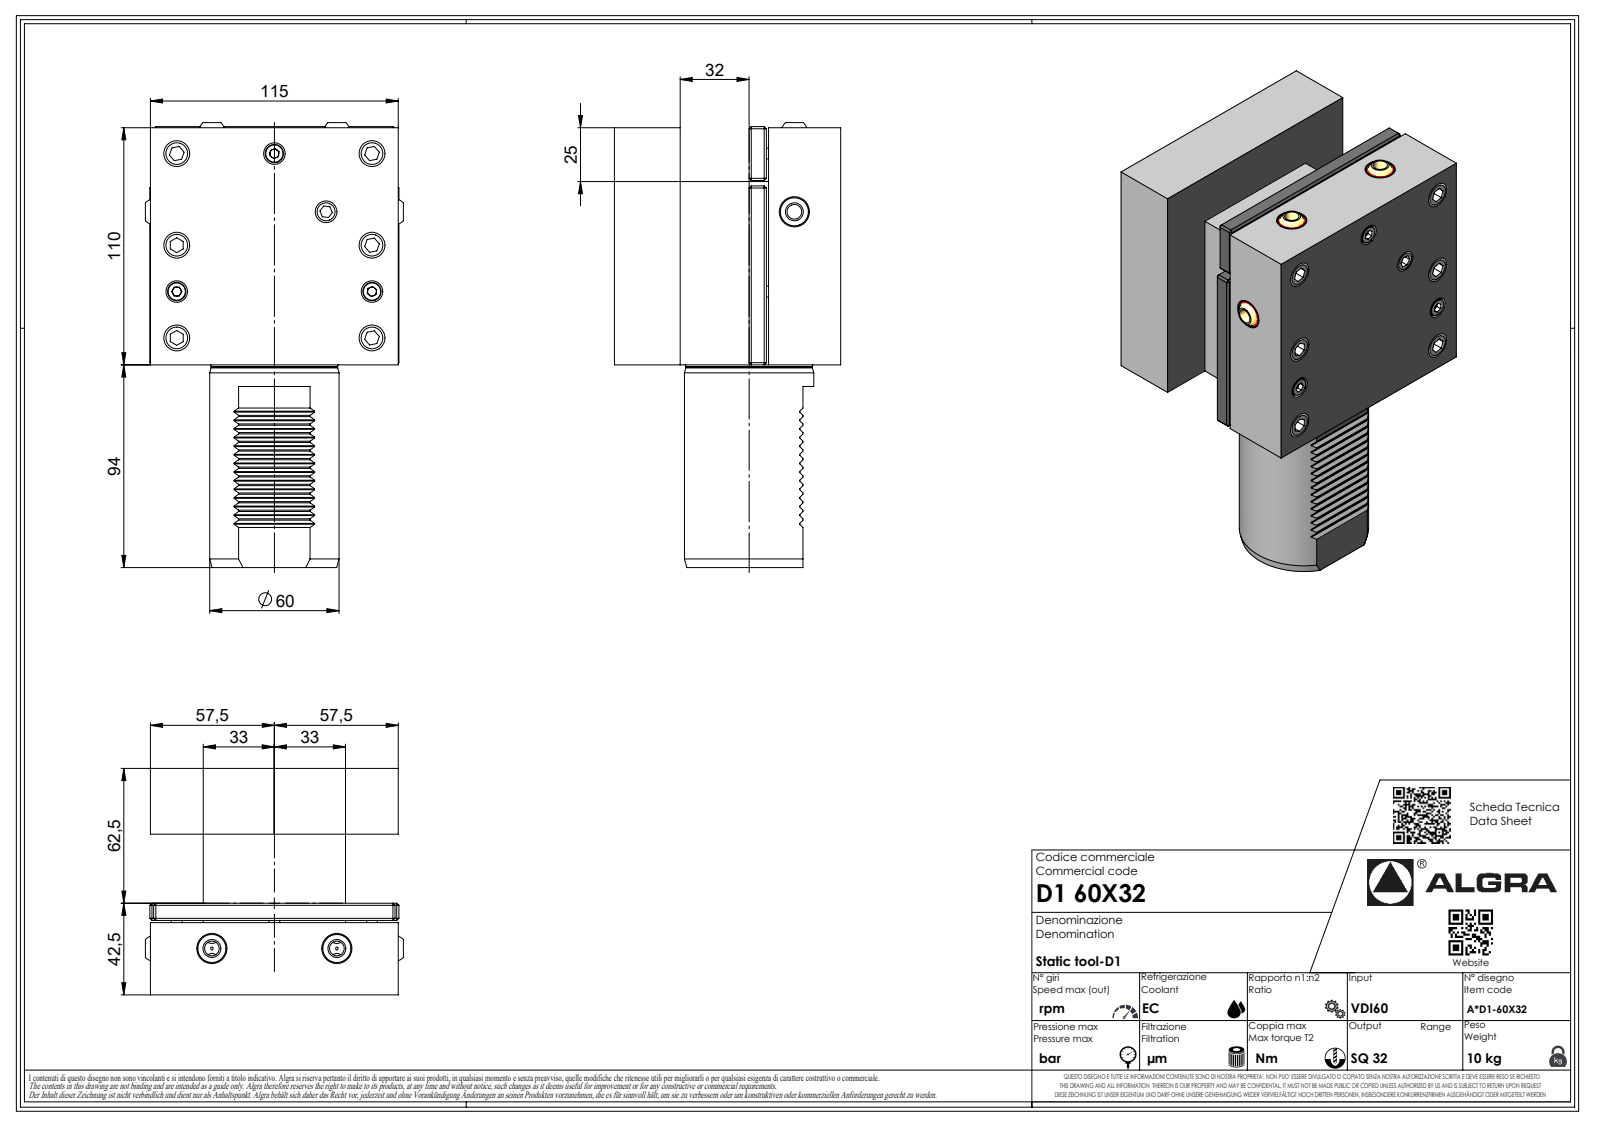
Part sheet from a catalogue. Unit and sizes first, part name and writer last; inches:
Units: inches
Overall size (bounding box): 8.125 × 4.714 × 4.134
Round holes (diameter × count): ⌀0.083 ×1
Round bosses / shafts (diameter × count): ⌀2.362 ×1, ⌀2.311 ×1, ⌀0.251 ×1, ⌀0.067 ×1
Partial cylindrical surfaces — rounded edges, fillets, slot ends (radius × count): R0.012 ×14, R0.013 ×7, R0.02 ×7, R0.146 ×7, R0.008 ×1
Main face-to-face distances: 4.134, 4.331, 1.201, 2.933, 4.528, 0.965, 2.461, 1.26, 1.673, 3.563
Volume: 82.69 in³ · Surface area: 160.7 in²
Bodies: 1 solid, 383 faces (282 planar, 42 cylindrical, 59 other)
Part name (STEP PRODUCT): D160X32
STEP written by: SolidWorks 2023 (AUTOMOTIVE_DESIGN)
